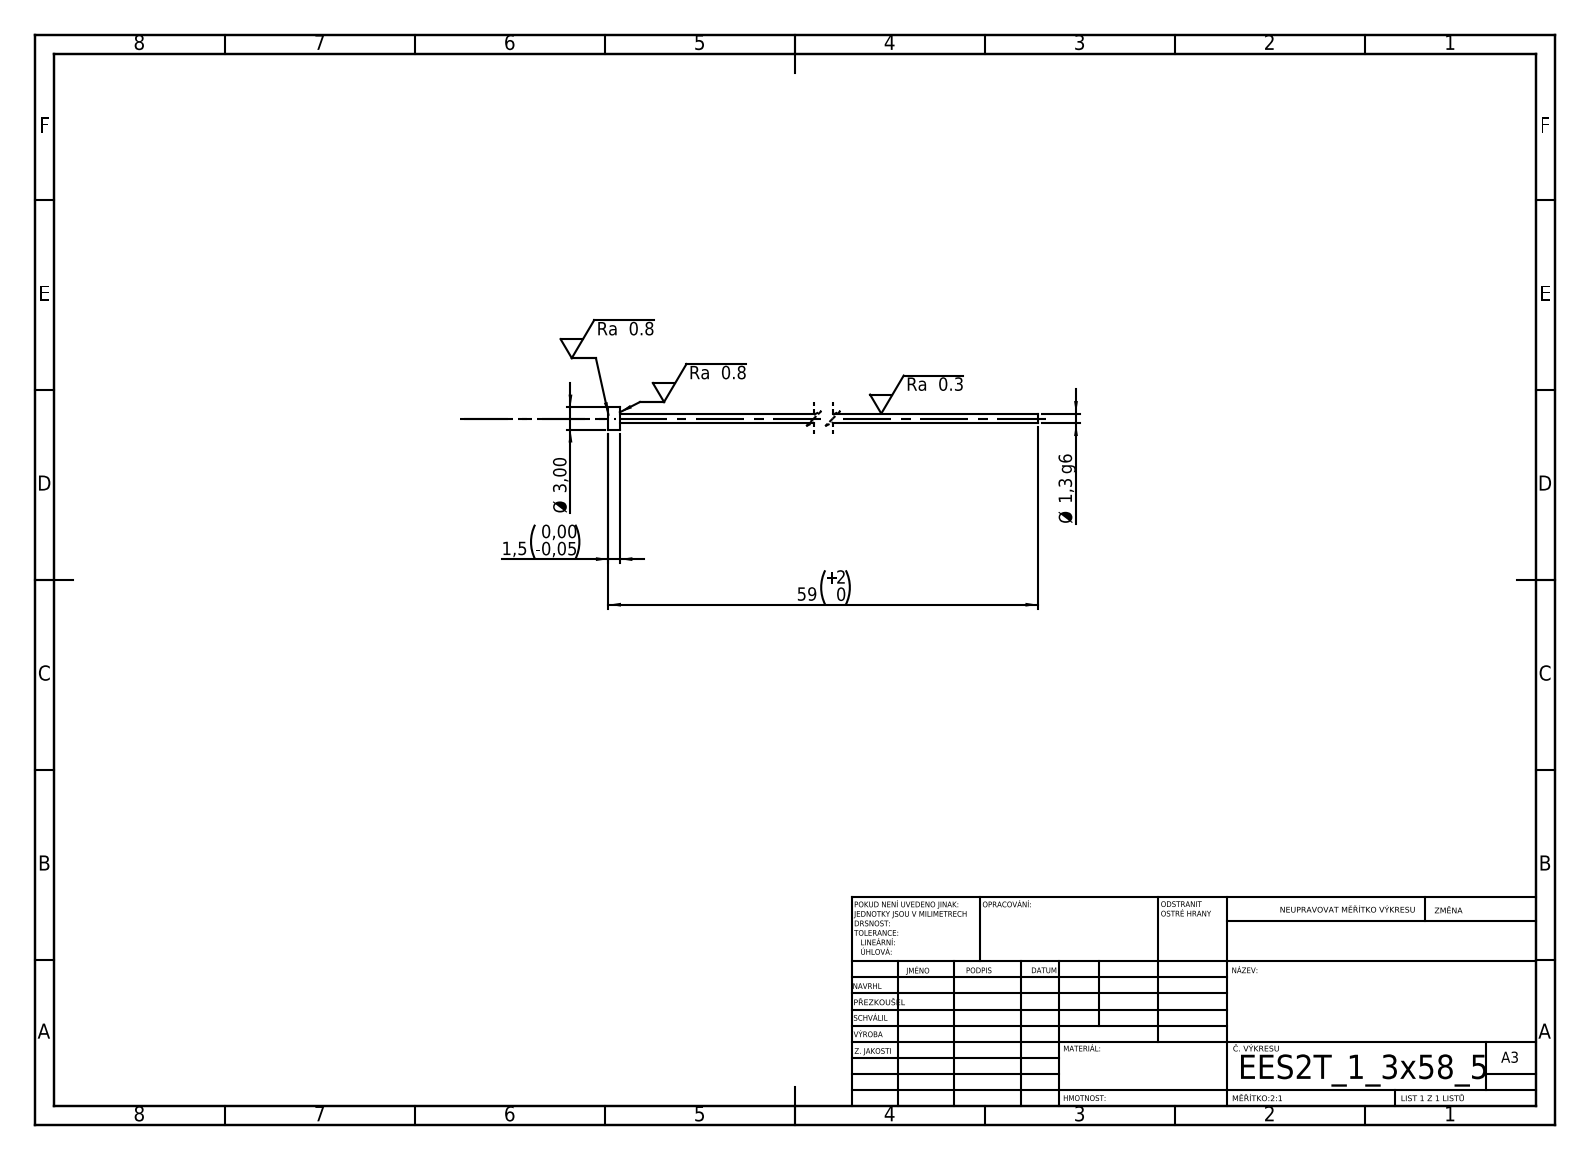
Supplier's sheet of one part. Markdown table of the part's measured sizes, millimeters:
| quantity | value |
| --- | --- |
| STEP written by | SolidWorks 2019 (CONFIG_CONTROL_DESIGN) |
| units | millimeters |
| bodies | 1 solid, 7 faces (3 planar, 4 cylindrical, 0 other) |
| overall size | 58.5 × 3 × 3 |
| volume | 86 mm³ |
| surface area | 261 mm² |
| round bosses / shafts (diameter × count) | 3 × 1, 1.3 × 1 |
| main face-to-face distances | 1.5, 58.5, 57 |
